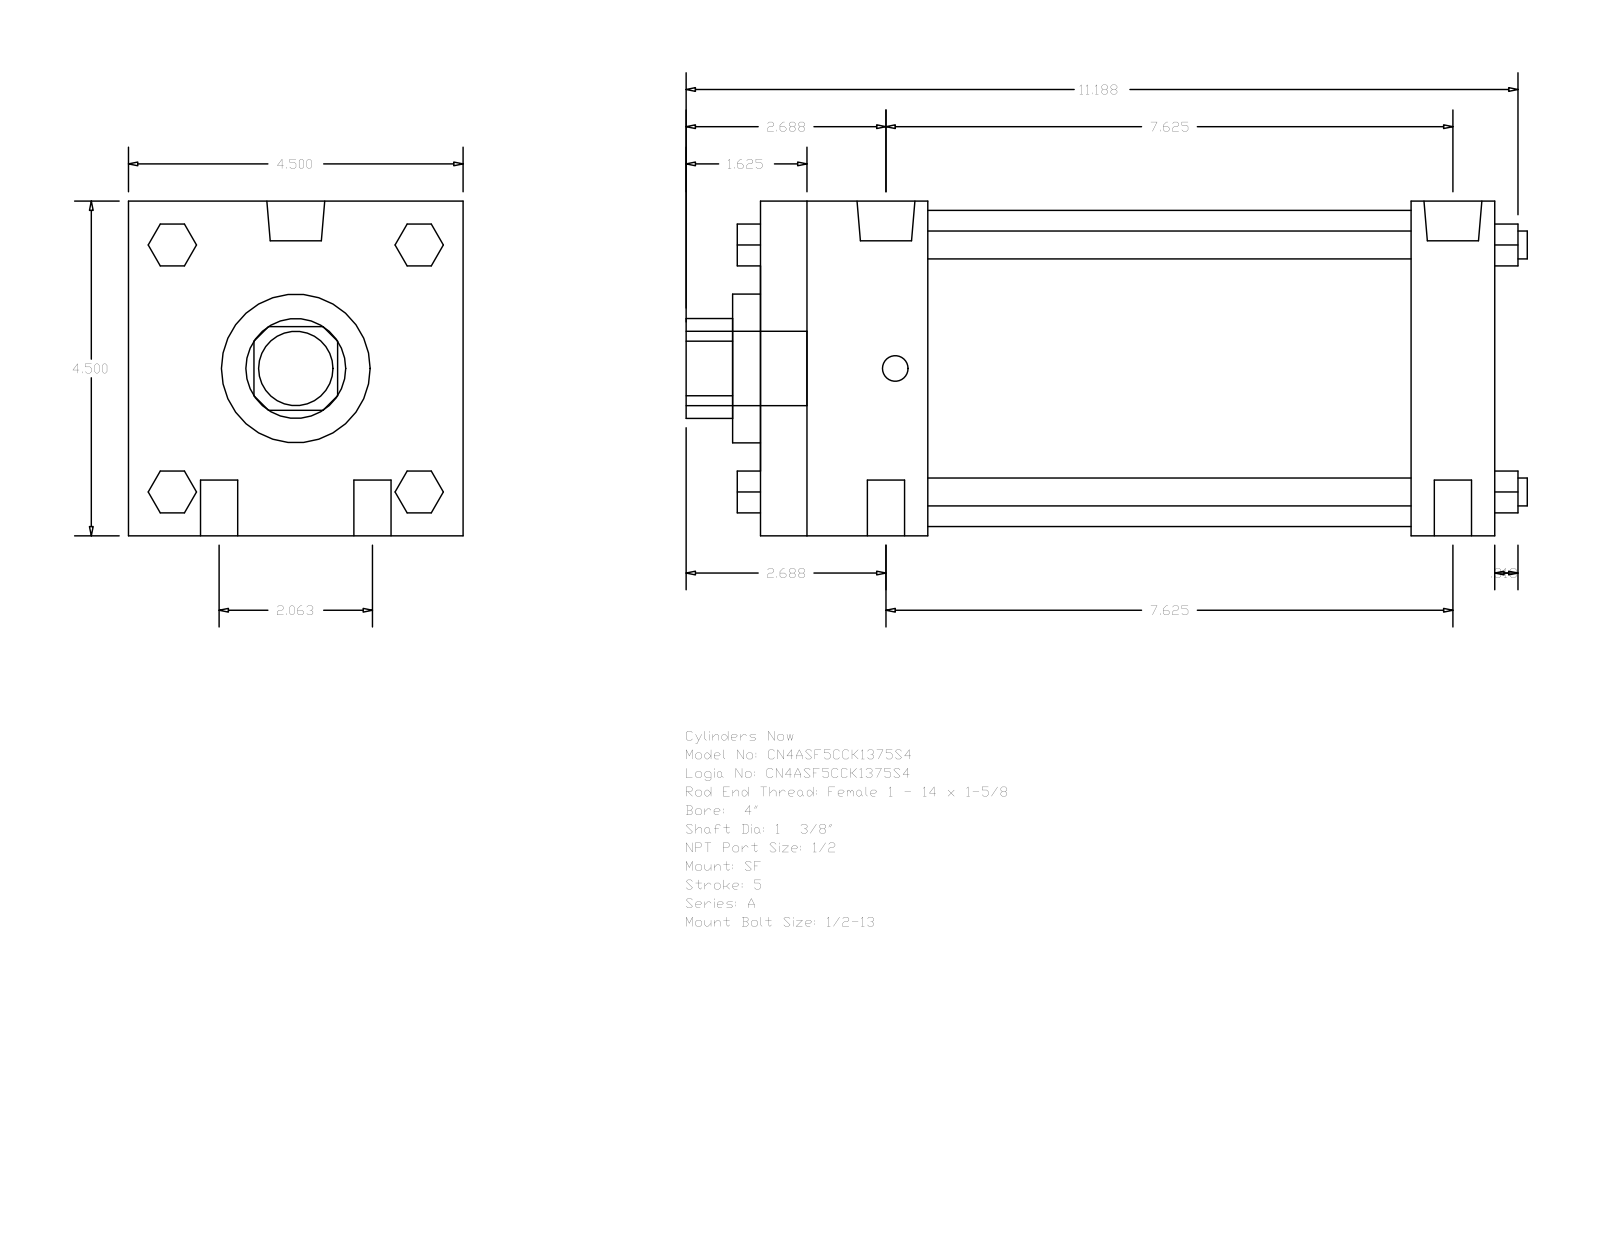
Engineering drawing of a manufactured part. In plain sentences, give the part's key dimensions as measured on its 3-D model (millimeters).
The part is named "A_SF__0400_1.375". Its 3-D file was written by "GSSL Pune (CONFIG_CONTROL_DESIGN)". It is 0 solids with 124 faces: 94 planar, 30 cylindrical and 0 other. Overall it measures 287.34 by 114.3 by 114.3 millimeters. Round holes: 1 of diameter 34.92, 1 of diameter 50.8, 1 of diameter 107.95. Round bosses or shafts: 4 of diameter 12.7, 4 of diameter 9.53, 2 of diameter 19.77, 2 of diameter 8.73, 1 of diameter 25.4. Partial cylindrical surfaces (rounded edges, fillets, slot ends): 1 of radius 17.06. The main face-to-face distances are 114.3, 250.83, 28.58, 222.25, 57.15, 165.1, 193.68, 14.29, 9.52, 66.67.
